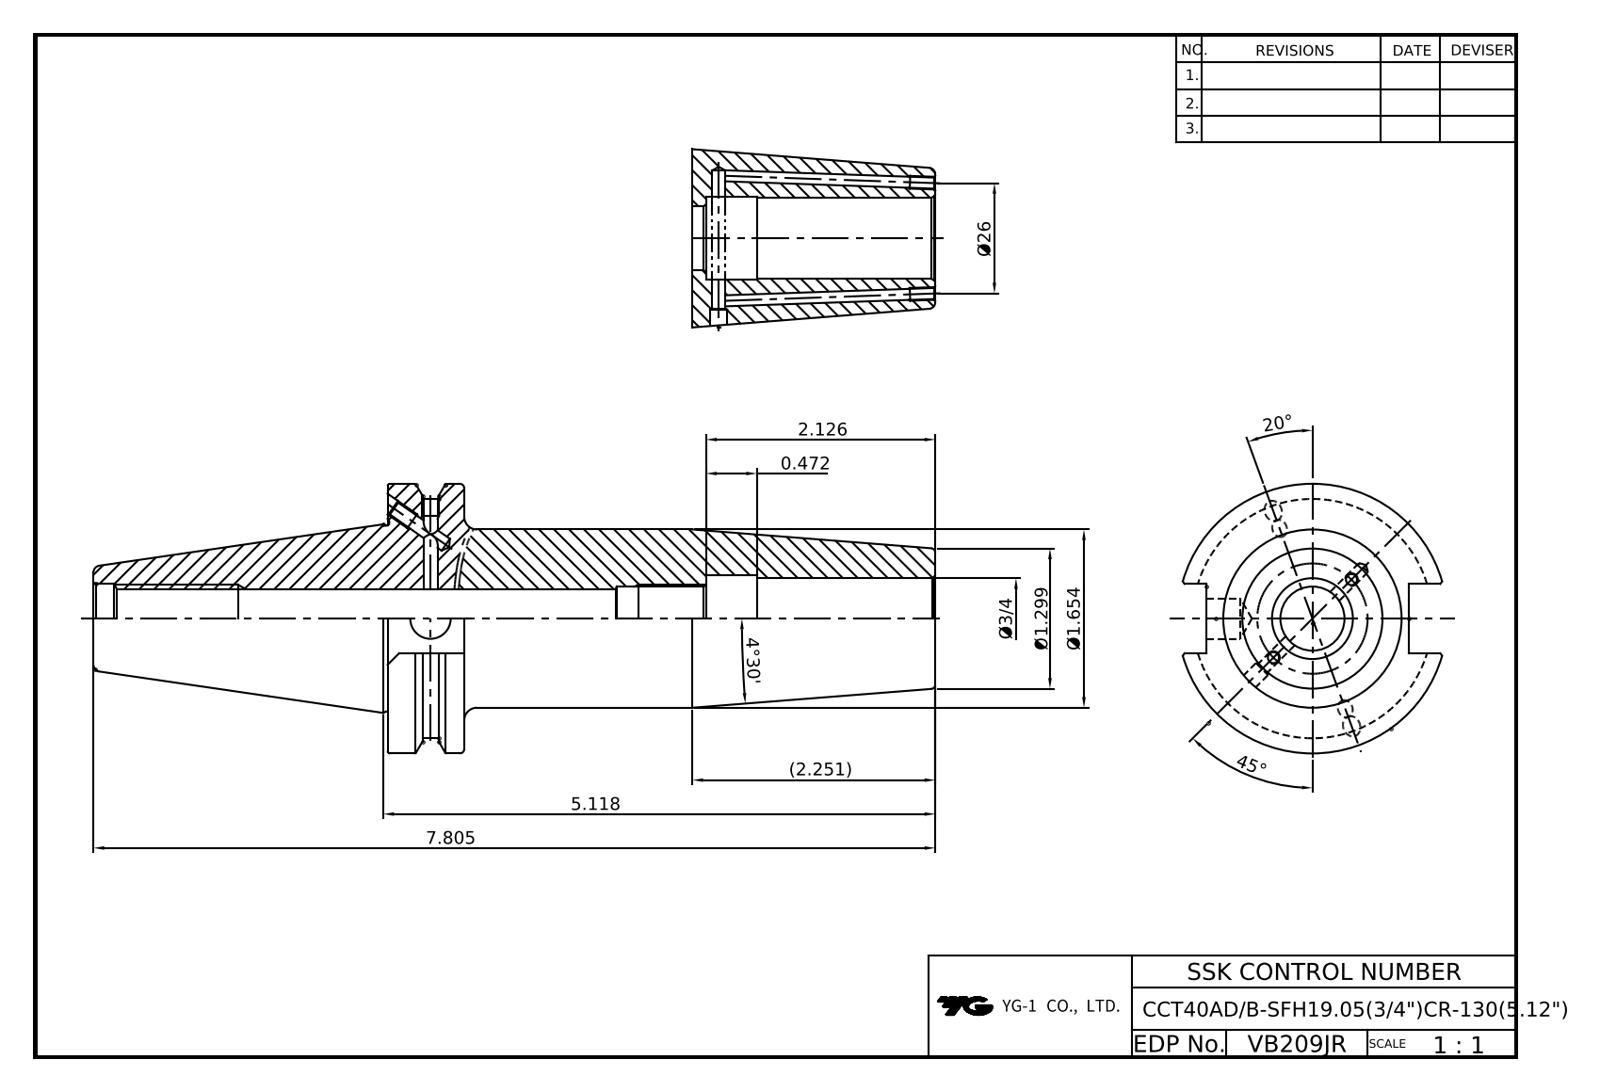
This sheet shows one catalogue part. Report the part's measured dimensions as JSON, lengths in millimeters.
{"part_name": "LO-CCT40ADB-SFH19.05CR-130", "step_written_by": "Autodesk Inventor 2026 (AUTOMOTIVE_DESIGN)", "units": "millimeters", "bodies": {"solids": 1, "faces": 88, "planar": 37, "cylindrical": 29, "other": 22}, "overall_size": [198.25, 63.5, 61.09], "volume_mm3": 216669, "surface_area_mm2": 40599, "round_holes": [[3.24, 4], [2.46, 2], [4, 2], [4.2, 2], [9.53, 1], [13.39, 1], [14.92, 1], [16.3, 1], [19.05, 1], [20.2, 1]], "round_bosses_or_shafts": [[63.5, 1], [42, 1]], "partial_cylinders_radius": [[28.15, 1]], "face_to_face_distances": [18.05, 129, 110.95, 47.6, 16.38, 69.25, 87.3, 198.25, 144.25, 75]}
